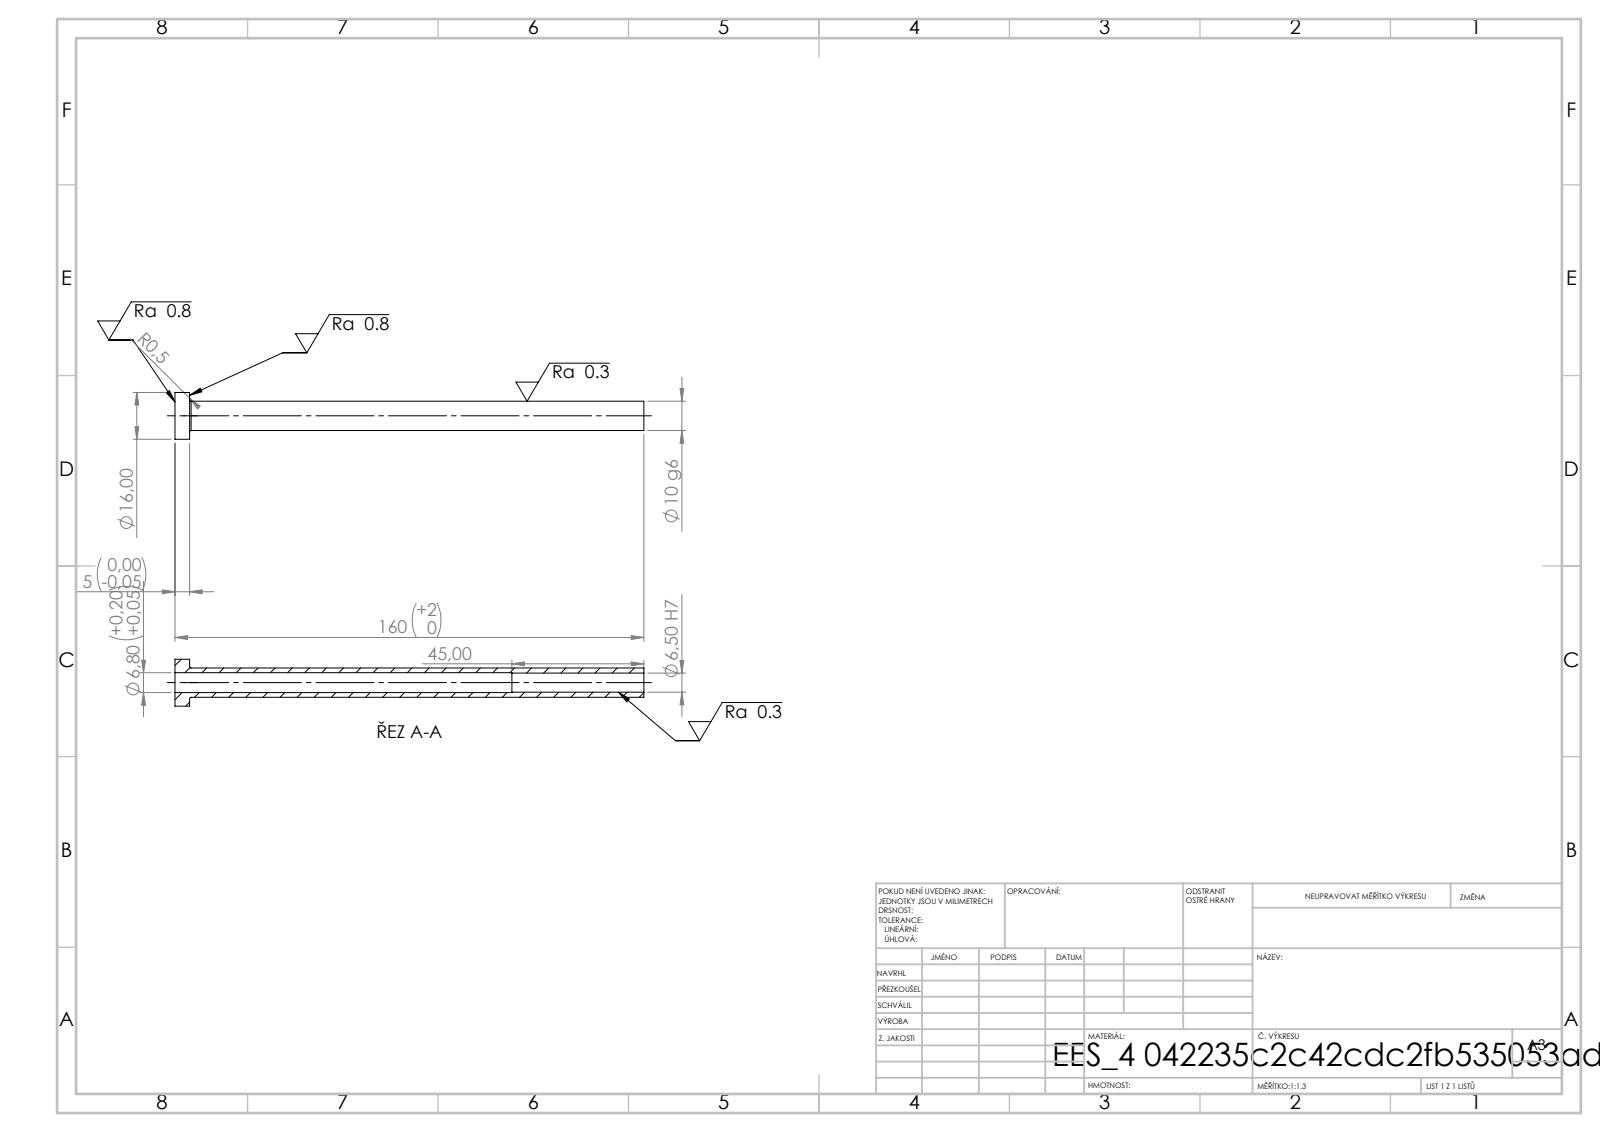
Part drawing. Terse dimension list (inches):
written by: SolidWorks 2019 (CONFIG_CONTROL_DESIGN)
unit: in
bodies: 1 solid, 14 faces (4 planar, 8 cylindrical, 2 other)
size: 6.299 × 0.63 × 0.63
volume: 0.458 in³; area: 13.68 in²
holes: 1× ⌀0.256, 1× ⌀0.268
bosses: 1× ⌀0.63, 1× ⌀0.394
face distances: 0.197, 6.299, 6.102, 4.528, 4.331, 1.772
